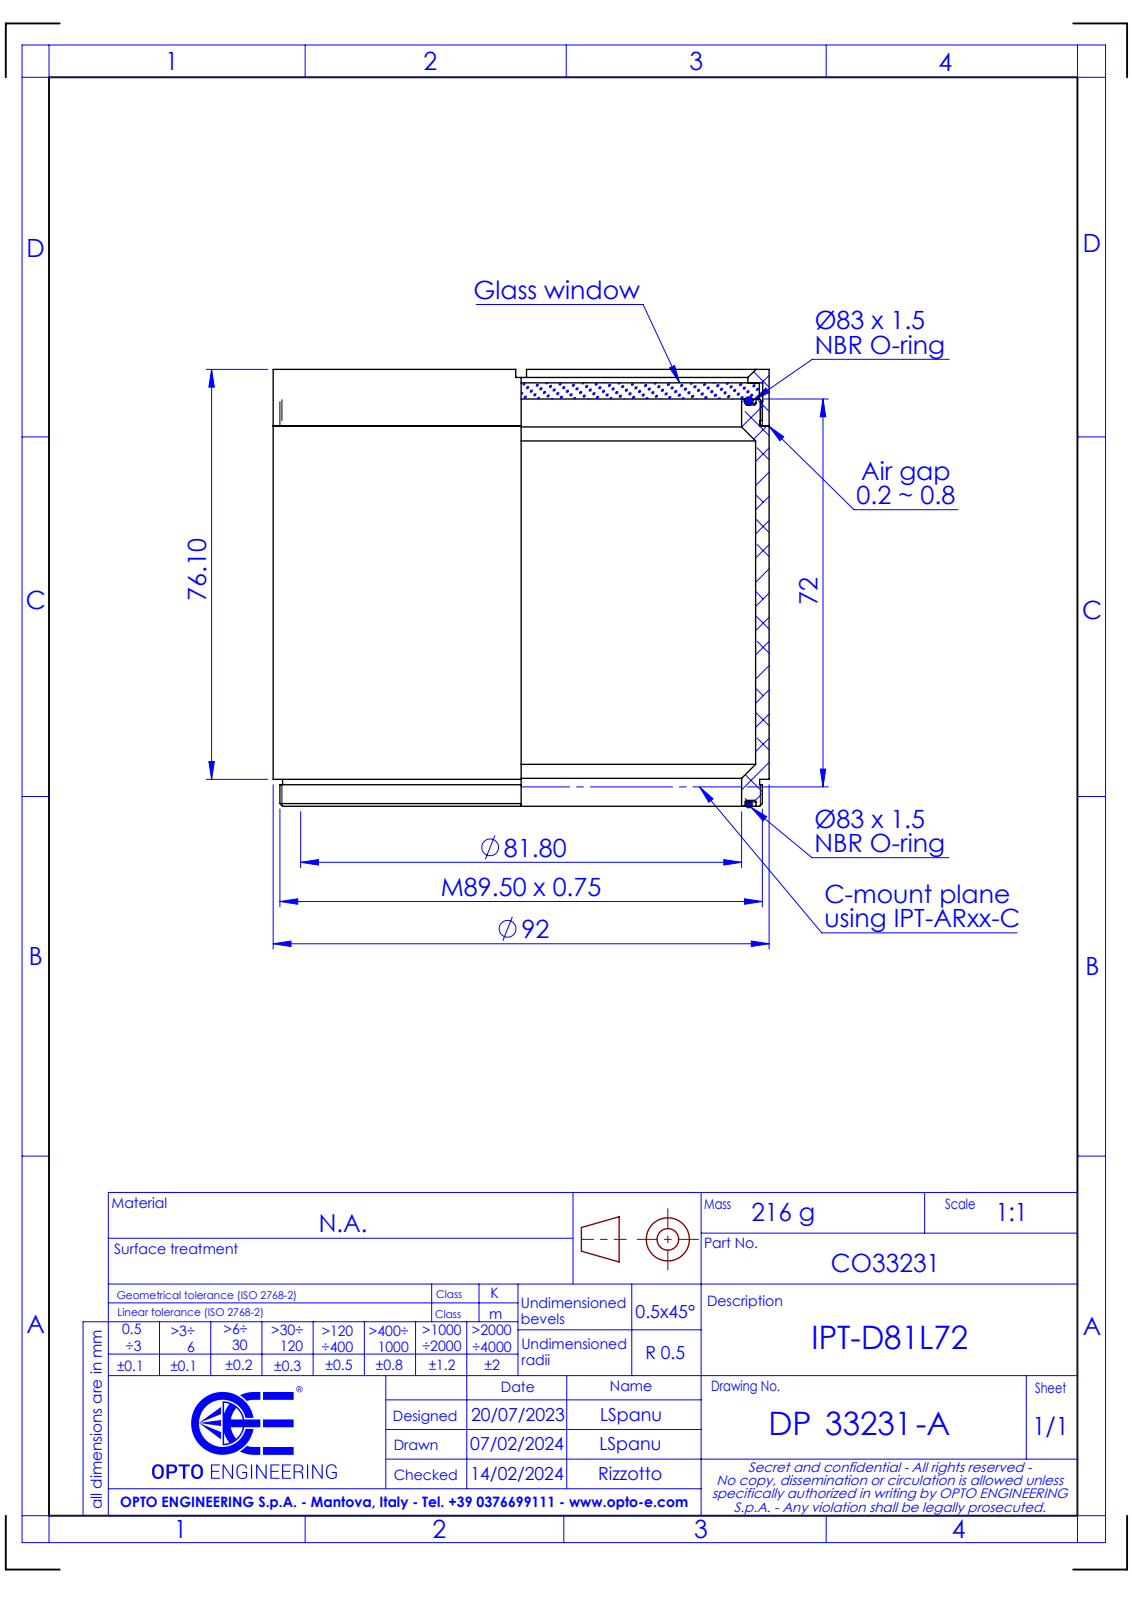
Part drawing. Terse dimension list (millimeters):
name: DP33231-A_IPT-D81L72
written by: SolidWorks 2021 (CONFIG_CONTROL_DESIGN)
unit: mm
bodies: 0 solids, 46 faces (16 planar, 18 cylindrical, 12 other)
size: 92 × 92 × 81.1
holes: 1× ⌀81.8, 1× ⌀84.15, 1× ⌀87, 1× ⌀87.15
bosses: 1× ⌀92, 1× ⌀89.5, 1× ⌀88.5, 1× ⌀83.15
face distances: 8, 10.5, 2.5, 65.6, 73.6, 76.1, 3.9, 69.5, 77.5, 80
